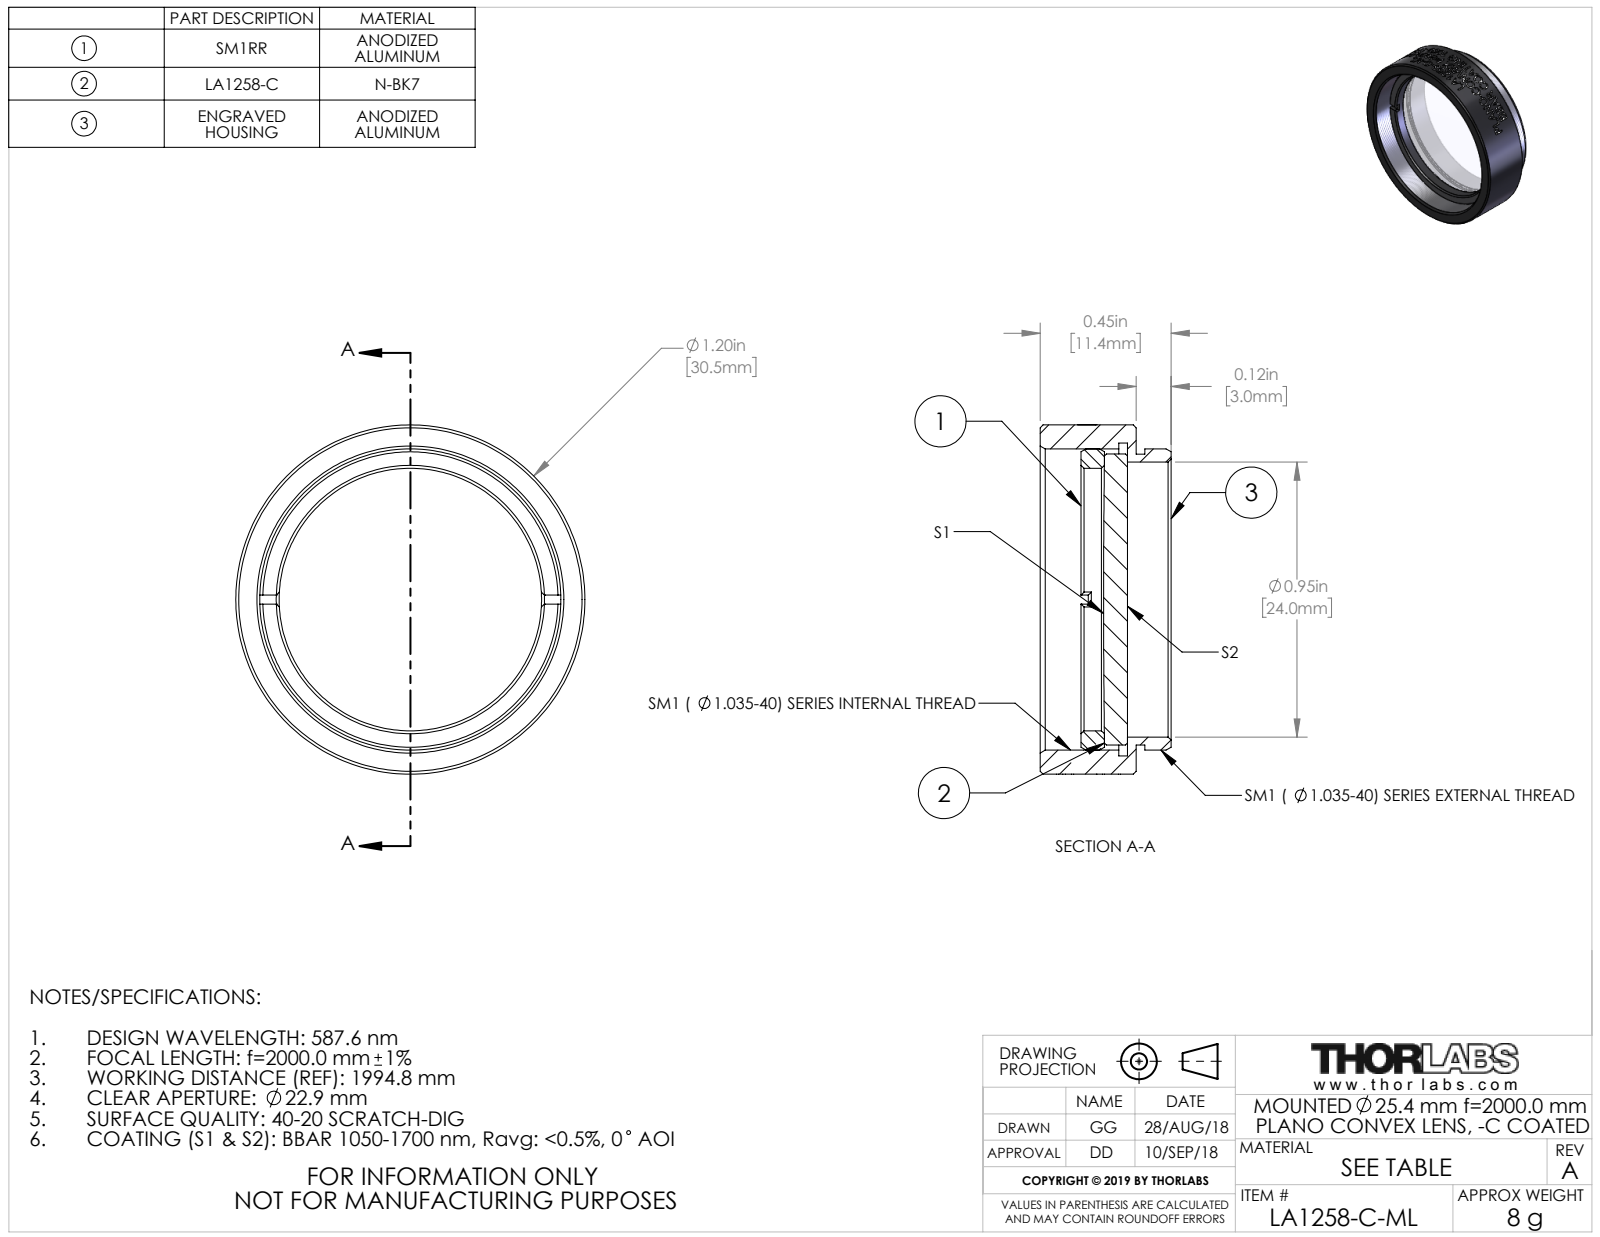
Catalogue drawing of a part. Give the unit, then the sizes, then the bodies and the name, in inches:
Units: inches
Overall size (bounding box): 1.2 × 1.2 × 0.45
Round holes (diameter × count): ⌀0.902 ×1, ⌀0.945 ×1, ⌀1.075 ×1
Round bosses / shafts (diameter × count): ⌀1.2 ×1, ⌀1.035 ×1, ⌀1 ×1, ⌀0.999 ×1
Main face-to-face distances: 0.03, 0.33, 0.3, 0.109, 0.079, 0.221, 0.189, 0.159, 0.08, 0.141
Volume: 0.19 in³ · Surface area: 6.659 in²
Bodies: 3 solids, 180 faces (20 planar, 132 cylindrical, 28 other)
Part name (STEP PRODUCT): TTN162142-E0W
STEP written by: SolidWorks 2018 (CONFIG_CONTROL_DESIGN)
